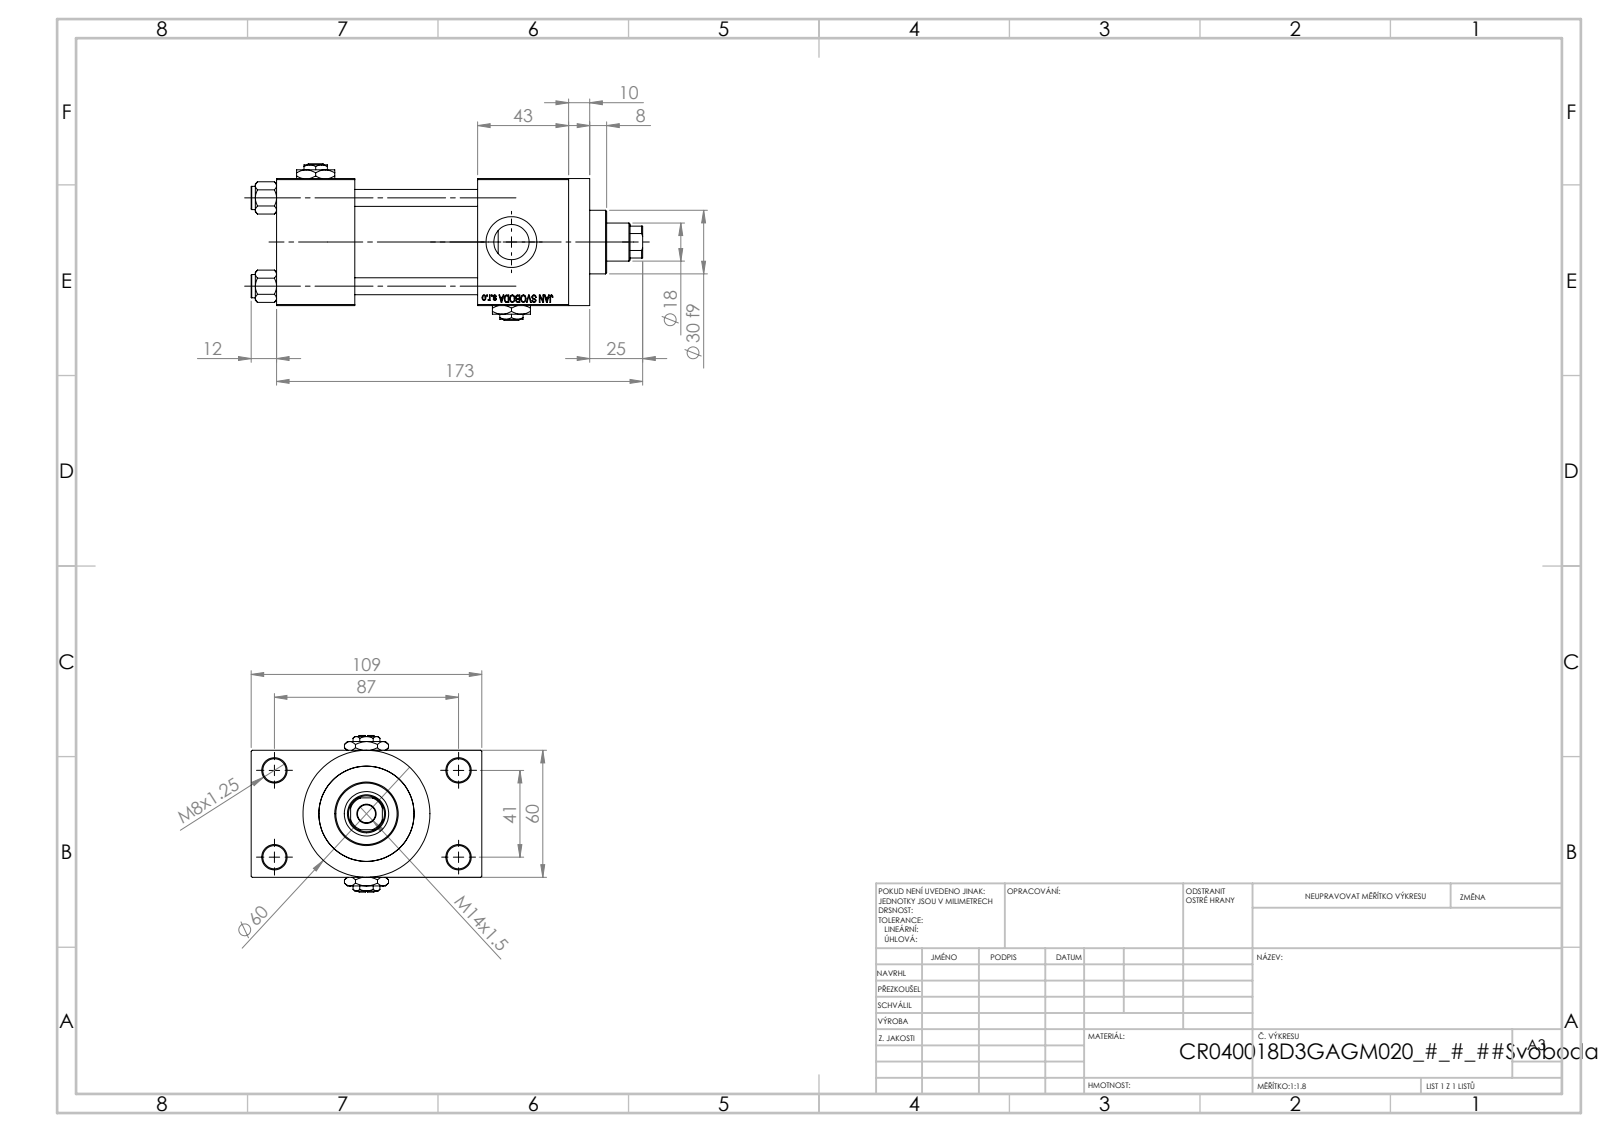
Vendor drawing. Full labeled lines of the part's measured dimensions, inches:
Part name (STEP PRODUCT): V215CR_D_Body; V215CR_D_TYCINKA; V215_VC_A; NUT_M5_D (+2 more)
STEP written by: SolidWorks 2019 (CONFIG_CONTROL_DESIGN)
Units: inches
Bodies: 13 solids, 1195 faces (544 planar, 93 cylindrical, 558 other)
Overall size (bounding box): 7.283 × 4.291 × 2.913
Volume: 31.33 in³ · Surface area: 192.8 in²
Round holes (diameter × count): ⌀0.315 ×4, ⌀0.433 ×4, ⌀0.656 ×3, ⌀0.945 ×3, ⌀0.276 ×2, ⌀0.335 ×1, ⌀0.709 ×1, ⌀0.827 ×1, ⌀1.22 ×1, ⌀1.575 ×1, ⌀1.772 ×1
Round bosses / shafts (diameter × count): ⌀0.433 ×4, ⌀2.362 ×1, ⌀1.811 ×1, ⌀1.181 ×1
Partial cylindrical surfaces — rounded edges, fillets, slot ends (radius × count): R0.335 ×1
Main face-to-face distances: 2.362, 0.965, 3.327, 2.283, 1.457, 3.74, 1.693, 5.433, 3.976, 0.394
Hole centre spacings: 0.892, 1.161, 1.642, 1.856, 1.893, 2.533, 3.011, 1.614
